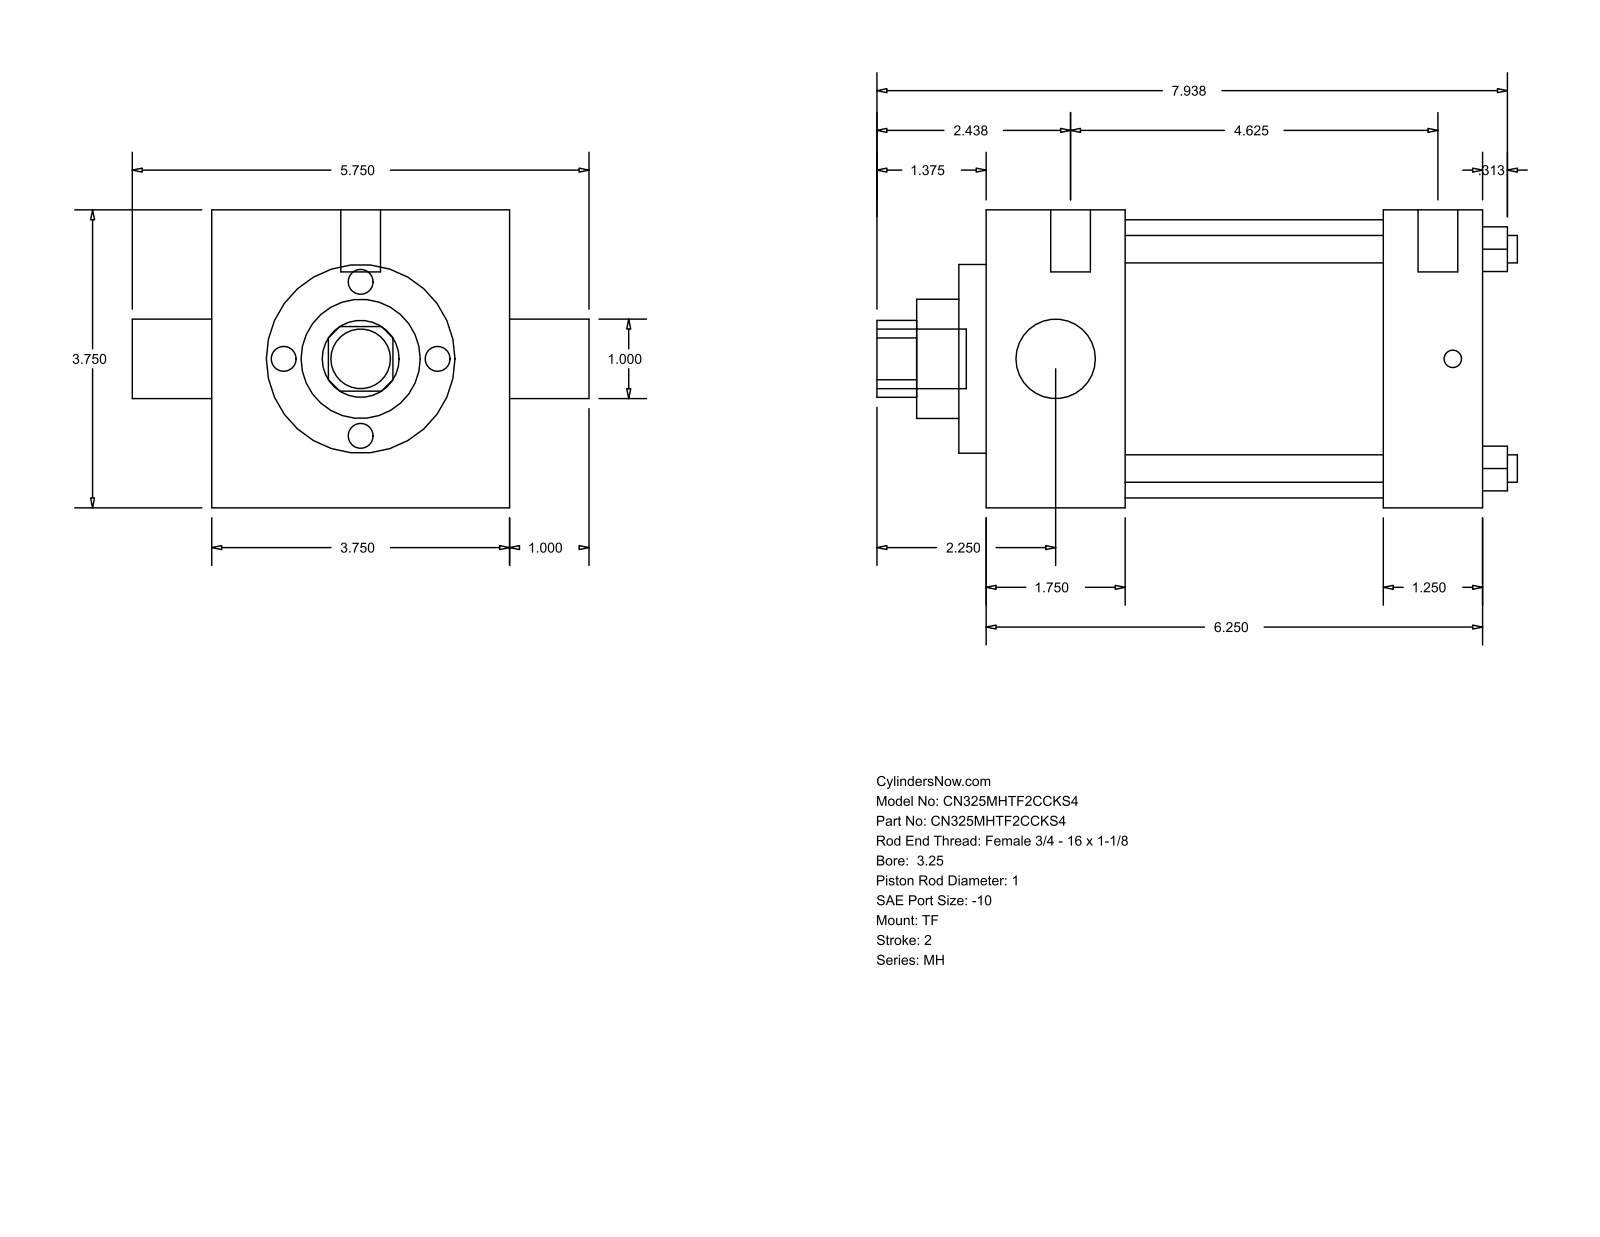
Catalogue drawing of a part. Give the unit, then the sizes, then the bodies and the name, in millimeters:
Units: millimetres
Overall size (bounding box): 204.79 × 146.05 × 95.25
Round holes (diameter × count): ⌀8.76 ×4, ⌀25.4 ×2, ⌀38.1 ×1, ⌀60.33 ×1, ⌀88.9 ×1
Round bosses / shafts (diameter × count): ⌀5.56 ×3, ⌀12.7 ×2, ⌀19.05 ×1
Partial cylindrical surfaces — rounded edges, fillets, slot ends (radius × count): R12.29 ×1
Main face-to-face distances: 95.24, 158.76, 44.46, 127.01, 82.55, 114.3, 31.75, 8.73, 53.19, 135.74
Hole centre spacings: 49.57, 70.1, 99.14
Bodies: 0 solids, 86 faces (61 planar, 25 cylindrical, 0 other)
Part name (STEP PRODUCT): MH_TF__0325_1
STEP written by: GSSL Pune (CONFIG_CONTROL_DESIGN)
